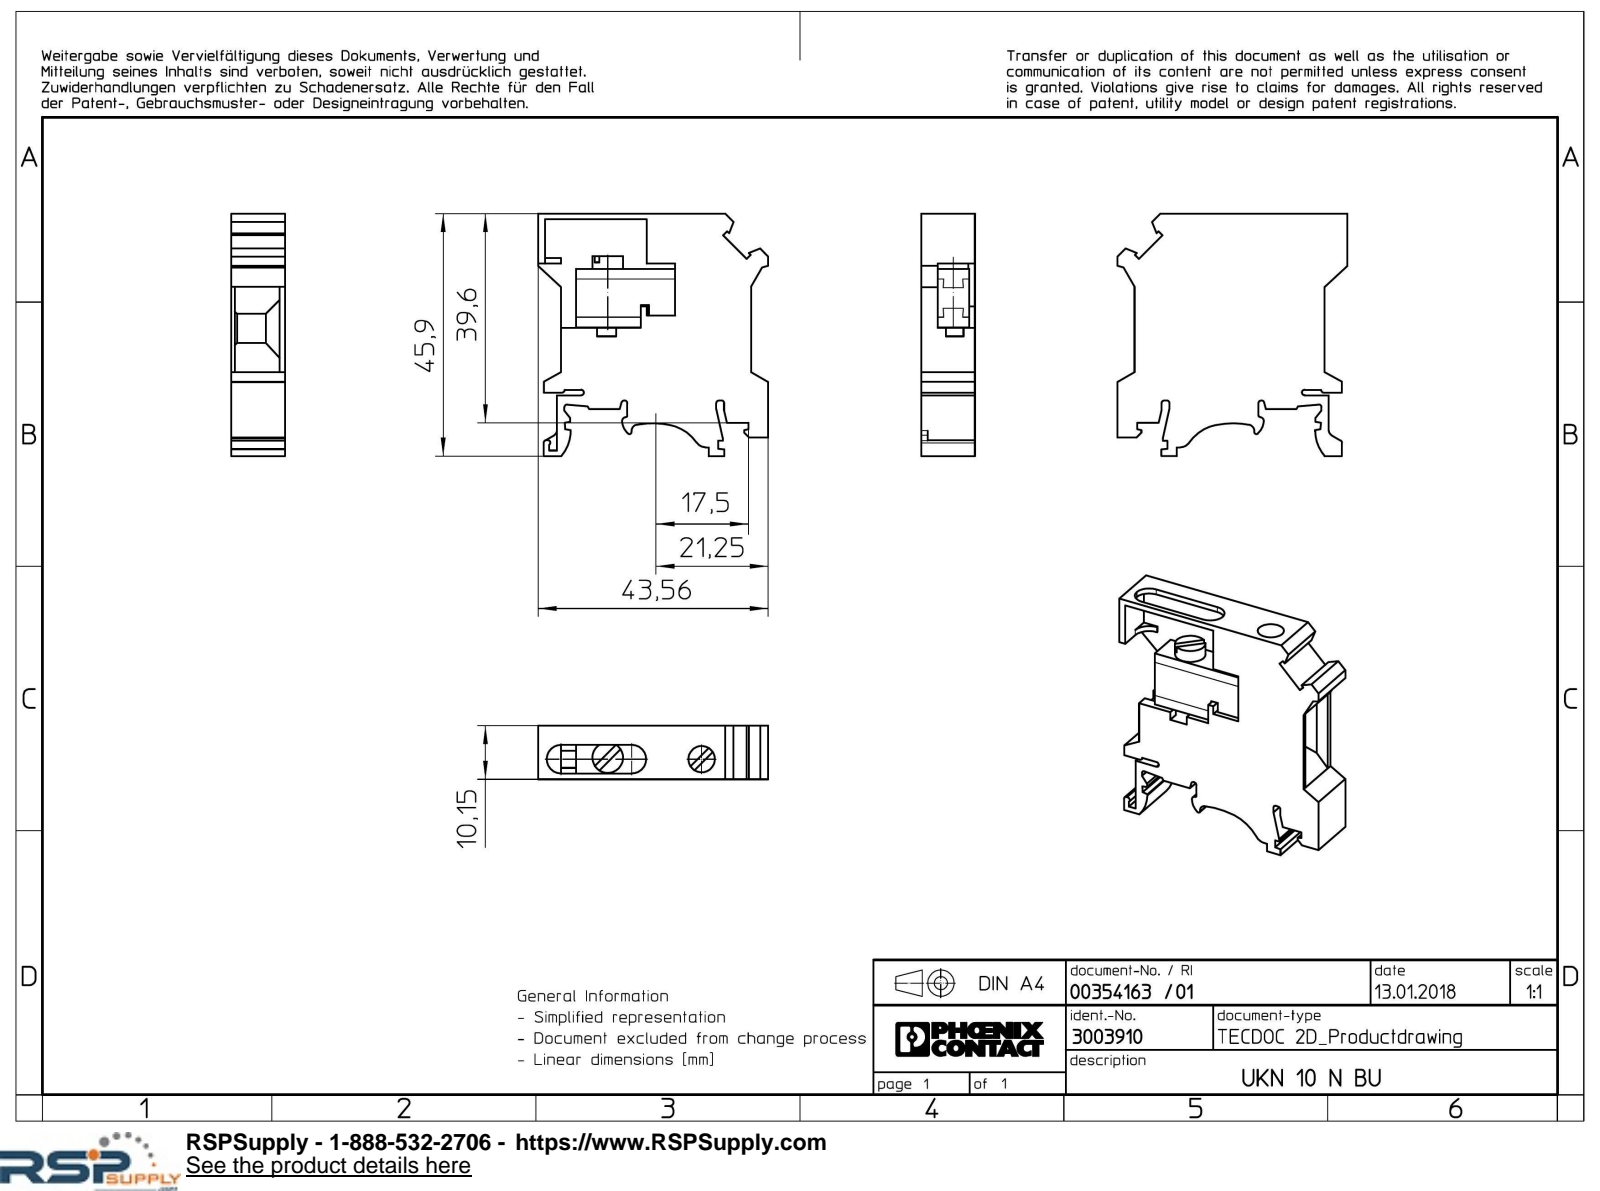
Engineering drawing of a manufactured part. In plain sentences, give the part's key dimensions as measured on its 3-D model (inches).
The part is named "UKN_10_N_BU-select". Its 3-D file was written by "Creo Elements/Direct Modeling 18.1I 14-Aug-2016 (C) Parametric Technology GmbH (AUTOMOTIVE_DESIGN)". It is 1 solid with 152 faces: 123 planar, 29 cylindrical and 0 other. Overall it measures 1.807 by 1.715 by 0.4 inches. Its volume is 0.778 cubic inches and its surface area 10.19 square inches. Round holes: 1 of diameter 0.197. Round bosses or shafts: 1 of diameter 0.228. Partial cylindrical surfaces (rounded edges, fillets, slot ends): 8 of radius 0.02, 2 of radius 0.106, 1 of radius 0.012, 1 of radius 0.016, 1 of radius 0.02, 1 of radius 0.021, 1 of radius 0.028, 1 of radius 0.039. The main face-to-face distances are 0.4, 0.041, 0.122, 0.358, 0.236, 0.278, 0.102, 1.545, 0.335, 1.433.
